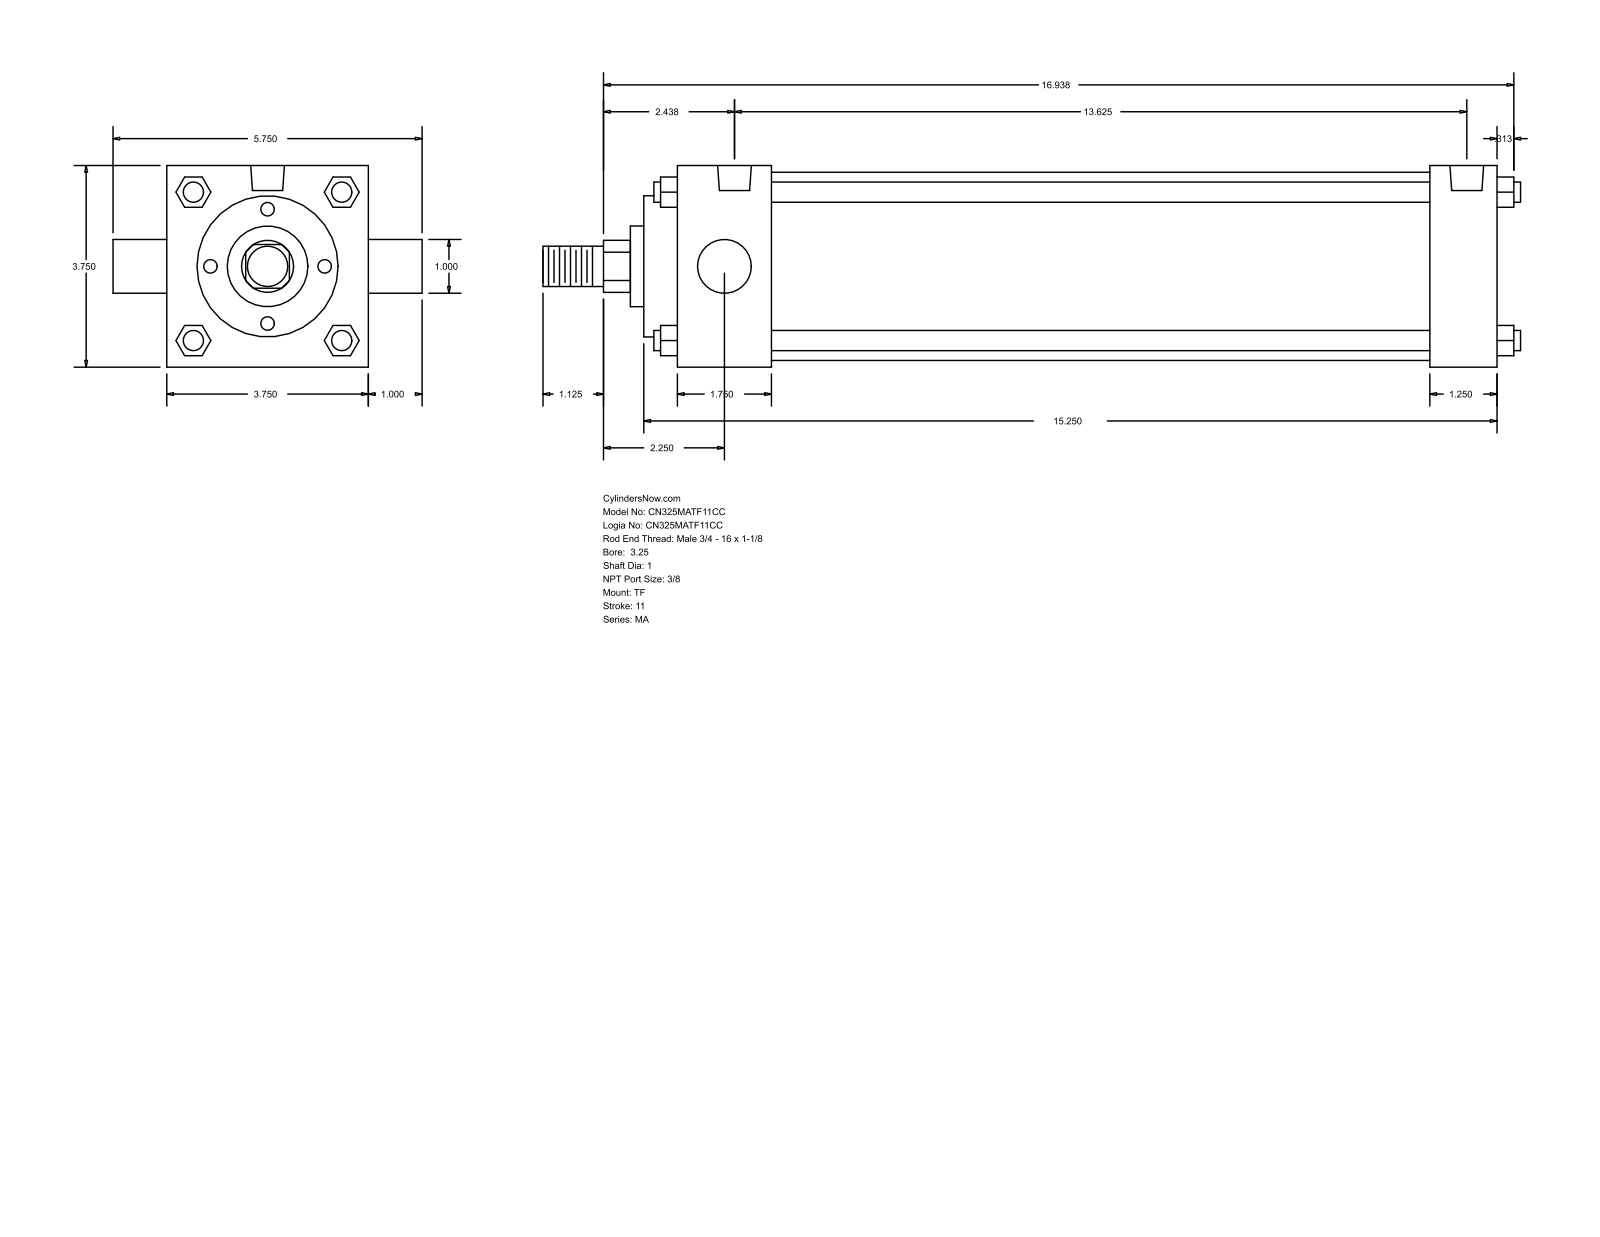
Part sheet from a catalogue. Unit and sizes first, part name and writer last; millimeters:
Units: millimetres
Overall size (bounding box): 461.96 × 146.05 × 95.25
Round holes (diameter × count): ⌀11.11 ×3, ⌀15.93 ×2
Round bosses / shafts (diameter × count): ⌀9.53 ×4, ⌀25.4 ×2, ⌀88.9 ×1, ⌀66.67 ×1, ⌀38.1 ×1, ⌀19.05 ×1
Partial cylindrical surfaces — rounded edges, fillets, slot ends (radius × count): R12.29 ×1
Main face-to-face distances: 95.24, 387.35, 403.22, 44.46, 355.6, 311.14, 342.89, 31.75, 15.87, 60.33
Hole centre spacings: 4.76, 341.32, 336.56, 346.08
Bodies: 0 solids, 122 faces (93 planar, 29 cylindrical, 0 other)
Part name (STEP PRODUCT): MA_TF__0325_1
STEP written by: GSSL Pune (CONFIG_CONTROL_DESIGN)
